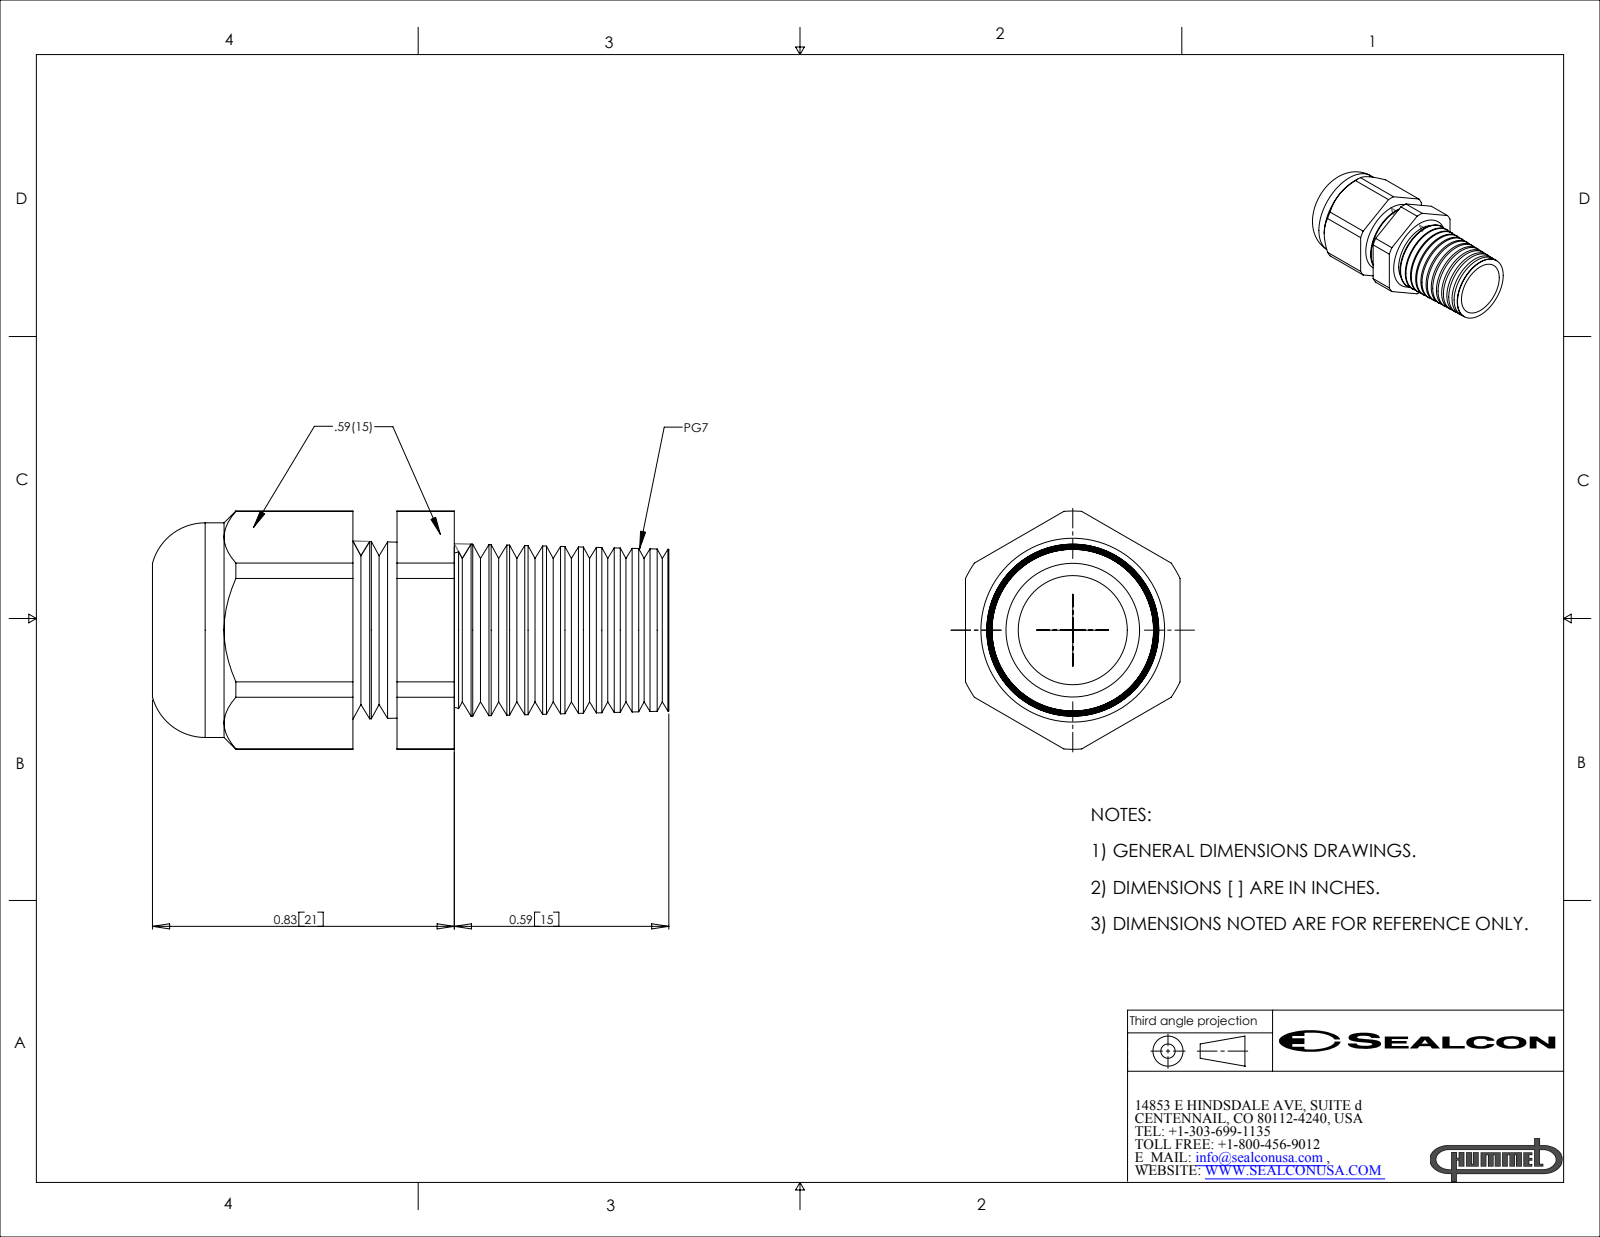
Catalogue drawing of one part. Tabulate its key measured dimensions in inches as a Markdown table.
| quantity | value |
| --- | --- |
| part name | CD07CA-BK |
| STEP written by | SolidWorks 2007 (CONFIG_CONTROL_DESIGN) |
| units | inches |
| bodies | 2 solids, 141 faces (19 planar, 22 cylindrical, 100 other) |
| overall size | 1.42 × 0.655 × 0.59 |
| volume | 0.19 in³ |
| surface area | 5.531 in² |
| round holes (diameter × count) | 0.3 × 1, 0.367 × 1 |
| round bosses / shafts (diameter × count) | 0.59 × 1 |
| partial cylindrical surfaces (radius × count) | 0.327 × 1 |
| main face-to-face distances | 0.59, 0.122, 0.279, 0.157, 0.354, 0.476, 0.633, 1.223, 0.869, 0.747 |
